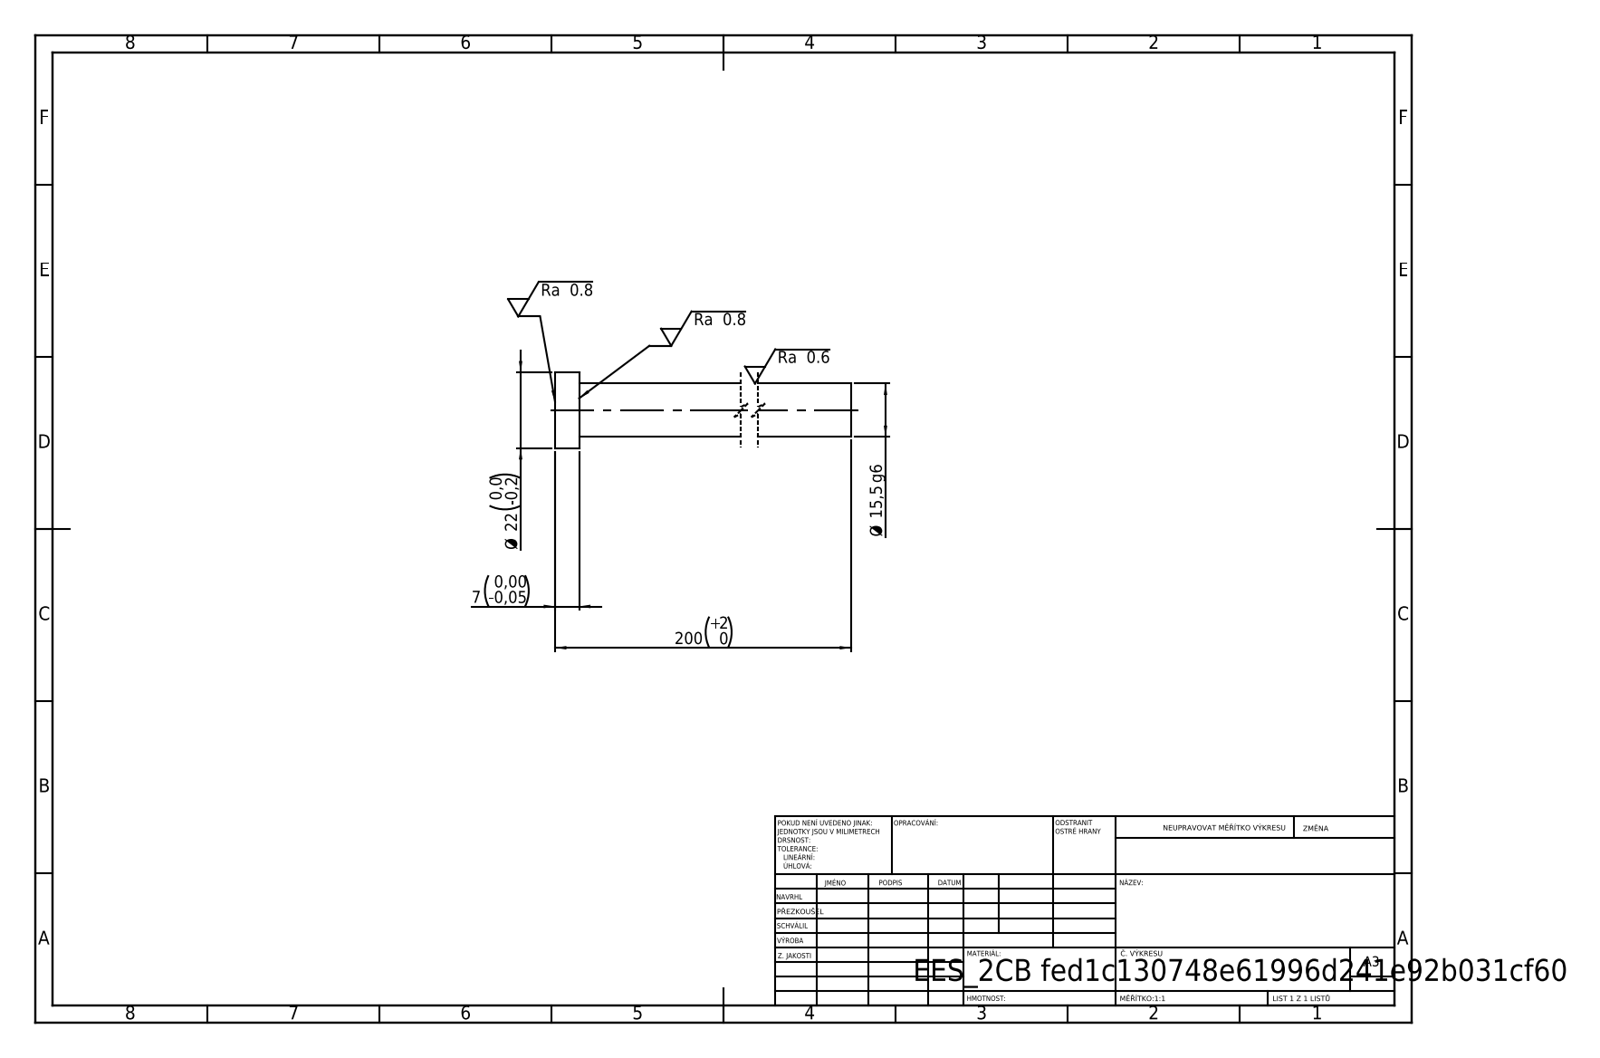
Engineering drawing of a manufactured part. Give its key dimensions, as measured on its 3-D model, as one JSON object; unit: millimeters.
{"step_written_by": "SolidWorks 2019 (CONFIG_CONTROL_DESIGN)", "units": "millimeters", "bodies": {"solids": 1, "faces": 7, "planar": 3, "cylindrical": 4, "other": 0}, "overall_size": [200, 22, 22], "volume_mm3": 39078, "surface_area_mm2": 10642, "round_bosses_or_shafts": [[22, 1], [15.5, 1]], "face_to_face_distances": [7, 200, 193]}
